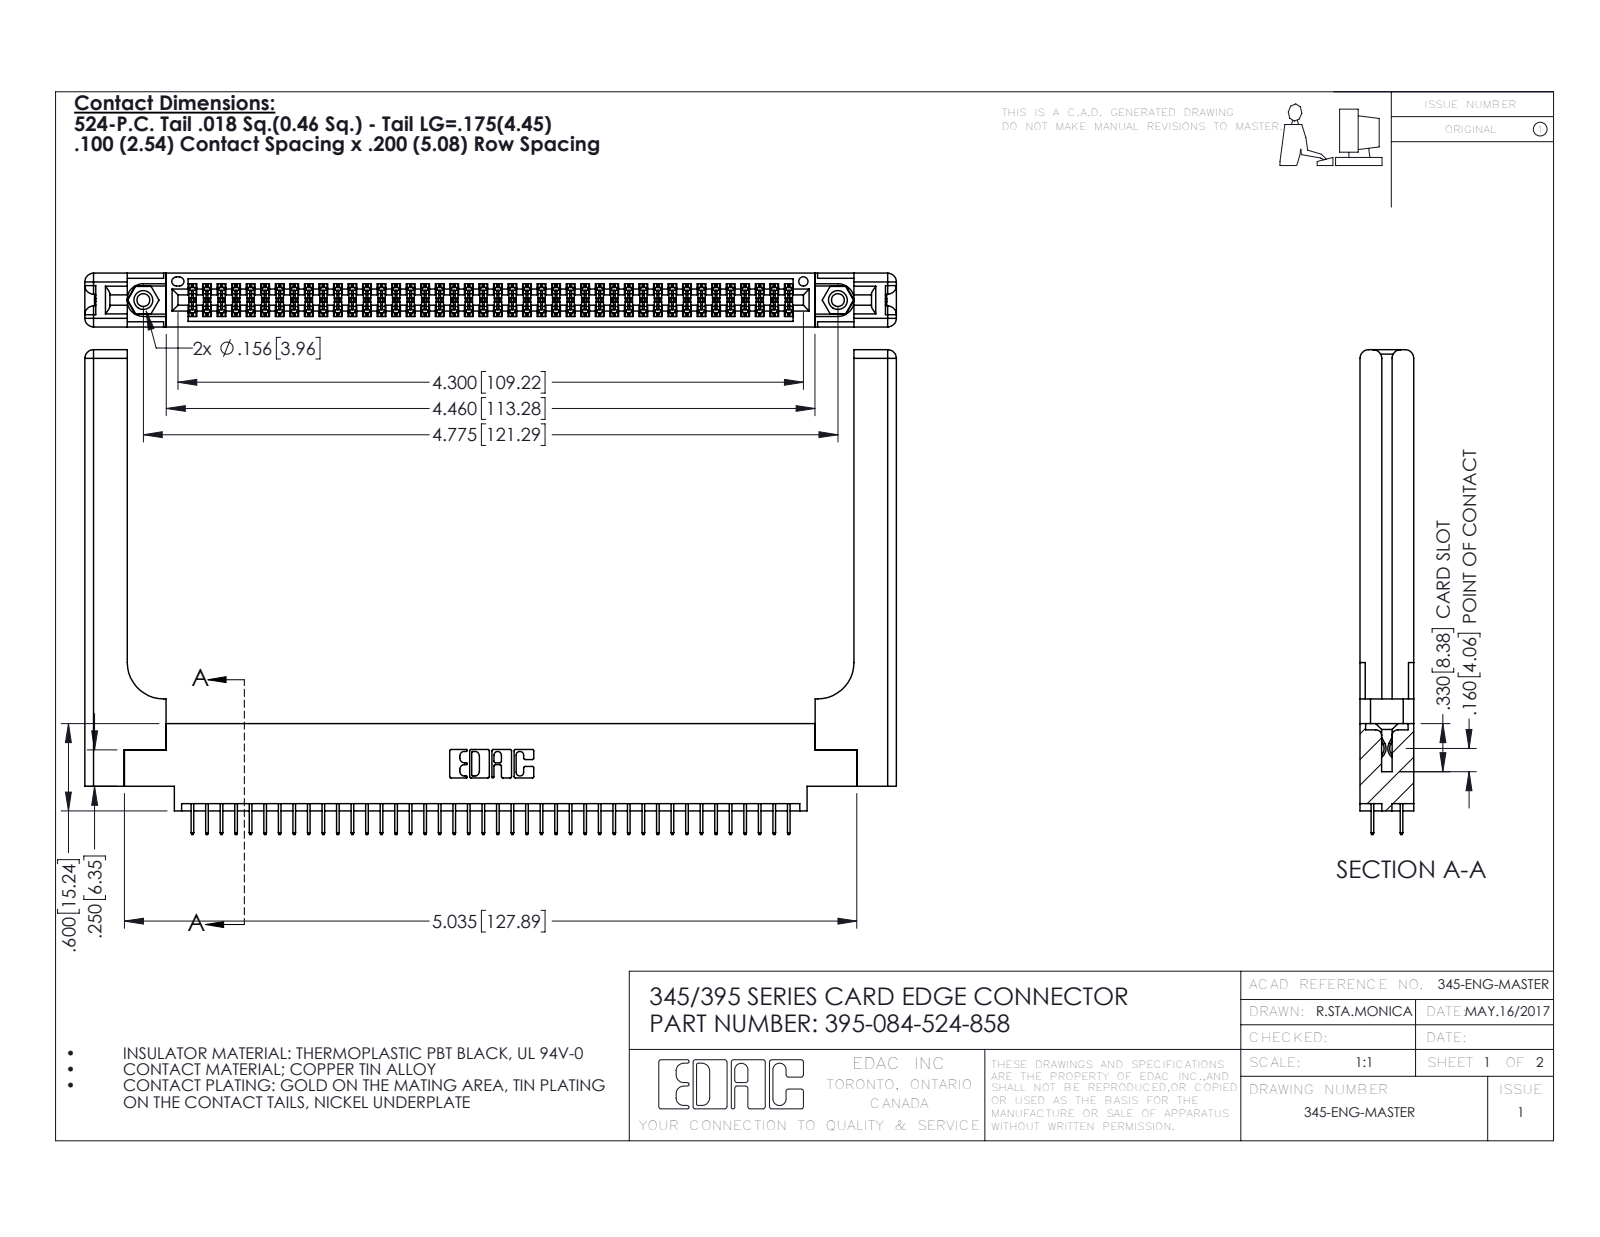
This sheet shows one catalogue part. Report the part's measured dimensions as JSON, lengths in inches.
{"part_name": "345-250-001_345-250-001-102; 345-292-001_345-293-124; 345 Part_0.170 Offset - 0.156 Dia-TH; 345-220-058_345-220-058 (+1 more)", "step_written_by": "SolidWorks 2016 (CONFIG_CONTROL_DESIGN)", "units": "inches", "bodies": {"solids": 89, "faces": 4922, "planar": 3508, "cylindrical": 1354, "other": 60}, "overall_size": [5.579, 3.332, 0.37], "volume_in3": 1.343, "surface_area_in2": 38.53, "round_holes": [[0.089, 2], [0.125, 2], [0.156, 2], [0.064, 1]], "round_bosses_or_shafts": [[0.155, 2]], "partial_cylinders_radius": [[0.006, 126], [0.01, 22], [0.06, 16], [0.007, 6], [0.031, 6], [0.026, 3], [0.014, 2], [0.019, 2]], "face_to_face_distances": [0.37, 0.072, 0.298, 0.2, 0.098, 0.272, 0.025, 0.225, 0.148, 0.15], "hole_center_spacings": [0.27, 4.539, 4.775]}
